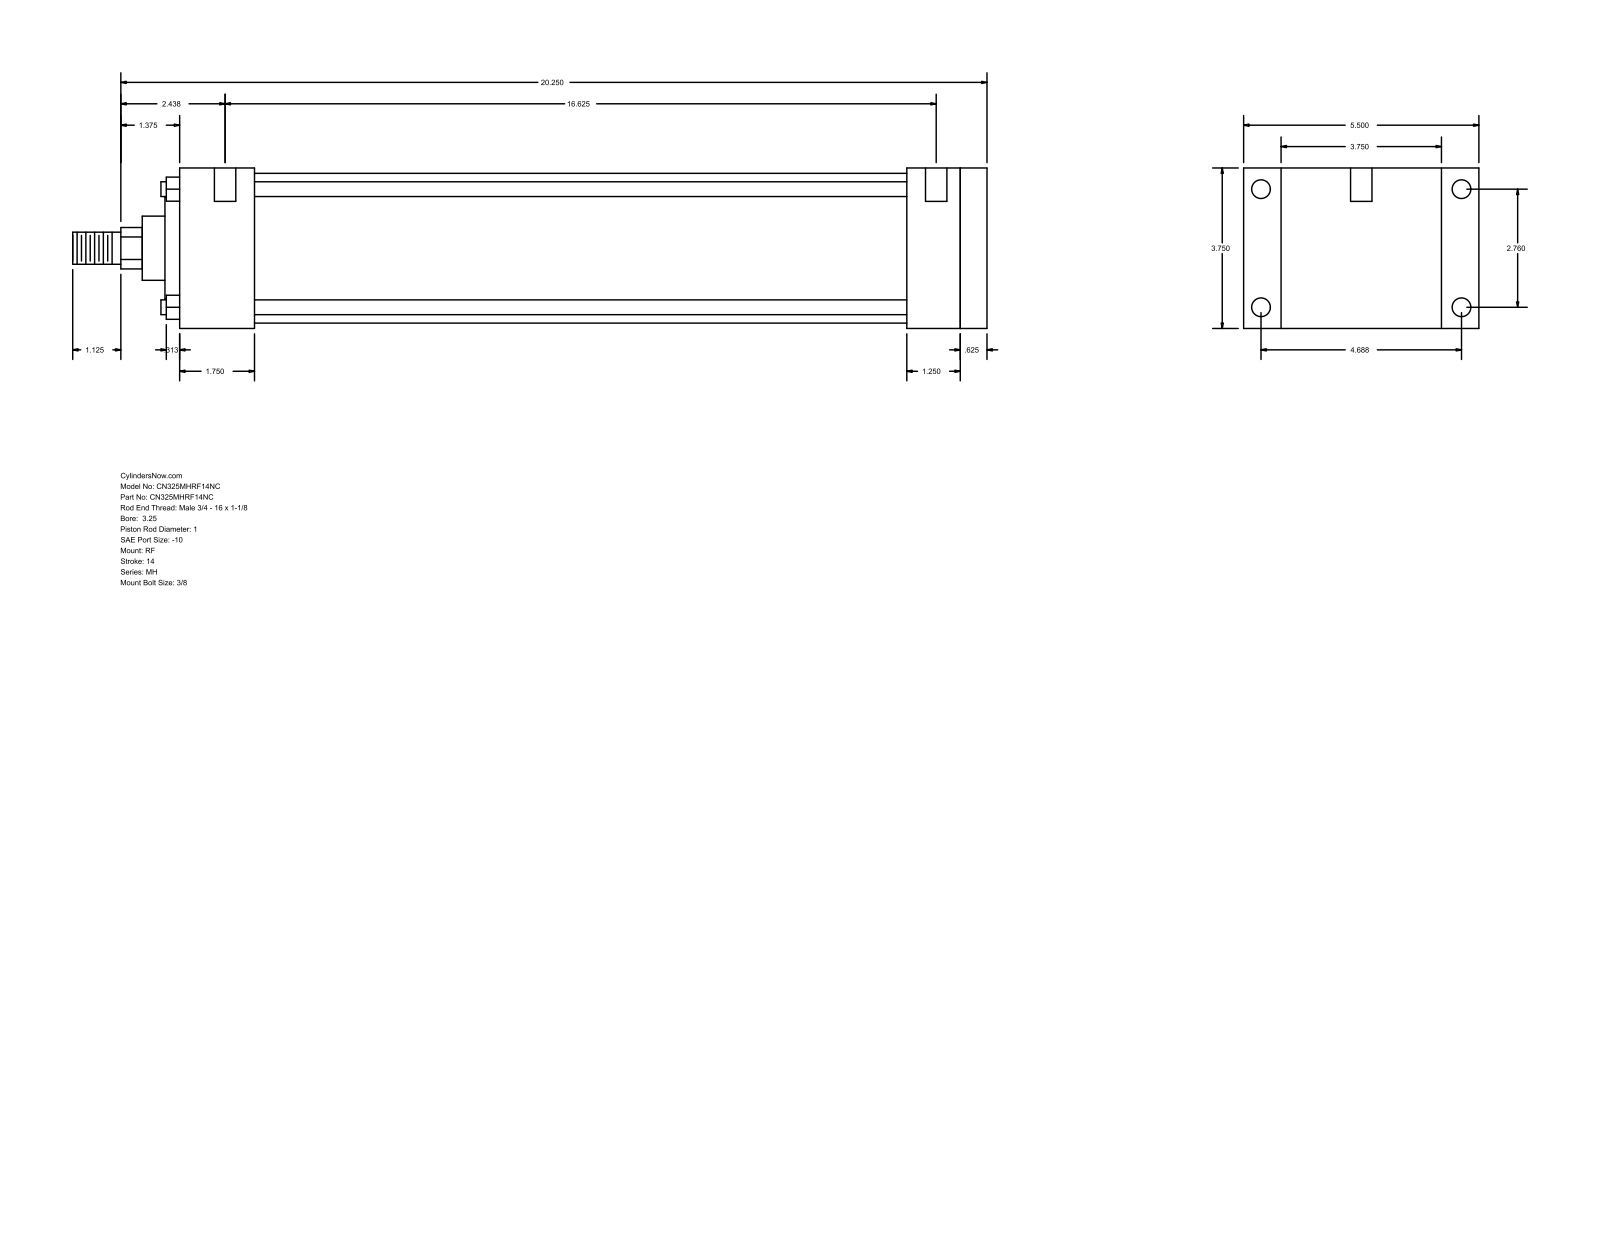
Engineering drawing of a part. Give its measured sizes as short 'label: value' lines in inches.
name: MH_RF__0325_1
written by: GSSL Pune (CONFIG_CONTROL_DESIGN)
unit: in
bodies: 0 solids, 94 faces (65 planar, 29 cylindrical, 0 other)
size: 21.375 × 5.5 × 3.75
holes: 4× ⌀0.219, 4× ⌀0.438, 2× ⌀0.5
bosses: 4× ⌀0.345, 1× ⌀3.5, 1× ⌀2.375, 1× ⌀1.5, 1× ⌀1, 1× ⌀0.75
rounds: 1× R0.484
face distances: 3.75, 18.875, 18.25, 0.625, 0.875, 4.625, 1.75, 16.5, 17.125, 17
hole spacings: 2.76, 4.687, 5.439, 16.875, 0.062, 0.187, 16.625, 16.687
